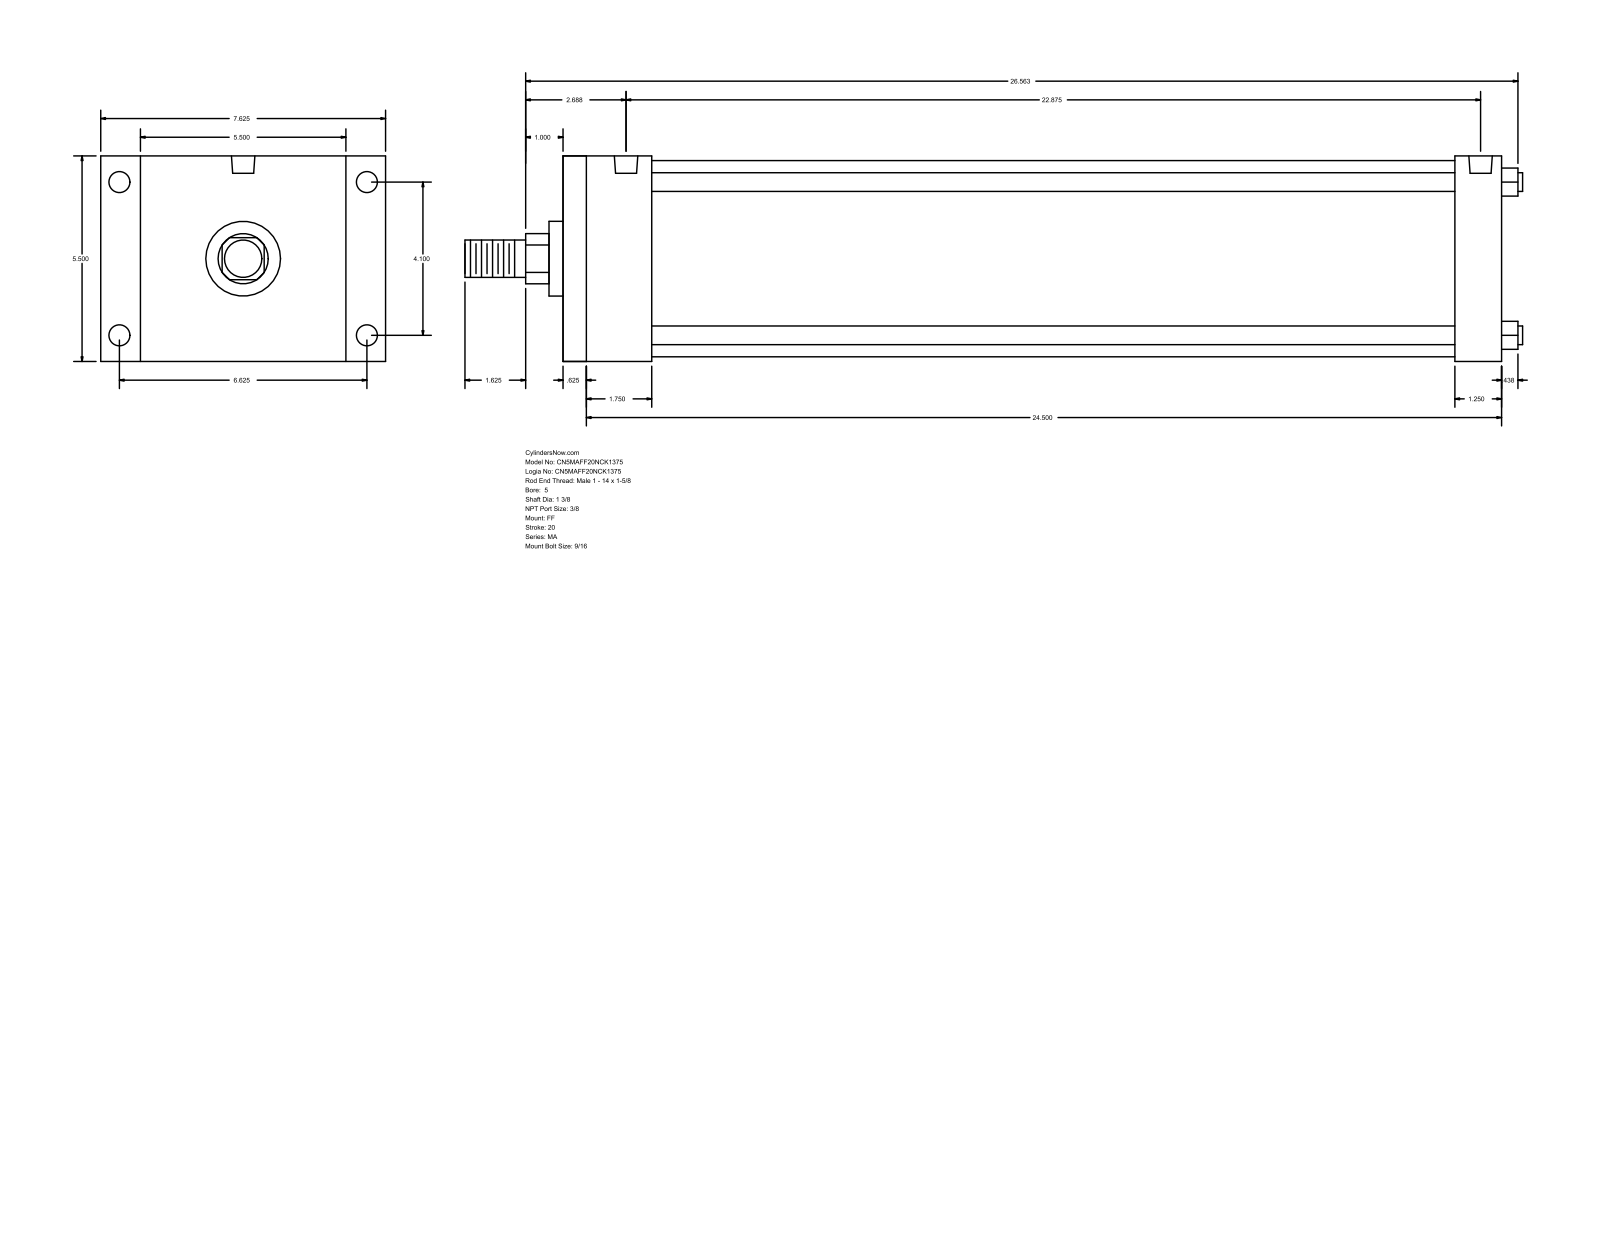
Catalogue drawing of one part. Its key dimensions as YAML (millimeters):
part_name: "MA_FF__0500_1.375"
step_written_by: "GSSL Pune (CONFIG_CONTROL_DESIGN)"
units: millimeters
bodies: {solids: 0, faces: 92, planar: 64, cylindrical: 28, other: 0}
overall_size: [719.14, 193.68, 139.7]
round_holes:
  - {diameter: 11.11, count: 4}
  - {diameter: 14.29, count: 4}
  - {diameter: 15.93, count: 2}
round_bosses_or_shafts:
  - {diameter: 12.7, count: 4}
  - {diameter: 133.35, count: 1}
  - {diameter: 50.8, count: 1}
  - {diameter: 34.92, count: 1}
  - {diameter: 25.4, count: 1}
partial_cylinders:
  - {radius: 17.06, count: 1}
face_to_face_distances: [139.7, 638.18, 15.87, 622.31, 606.43, 590.56, 31.75, 60.32, 44.45, 546.11]
hole_center_spacings: [4.77, 104.14, 168.28, 197.9, 571.49, 576.26, 581.03]
